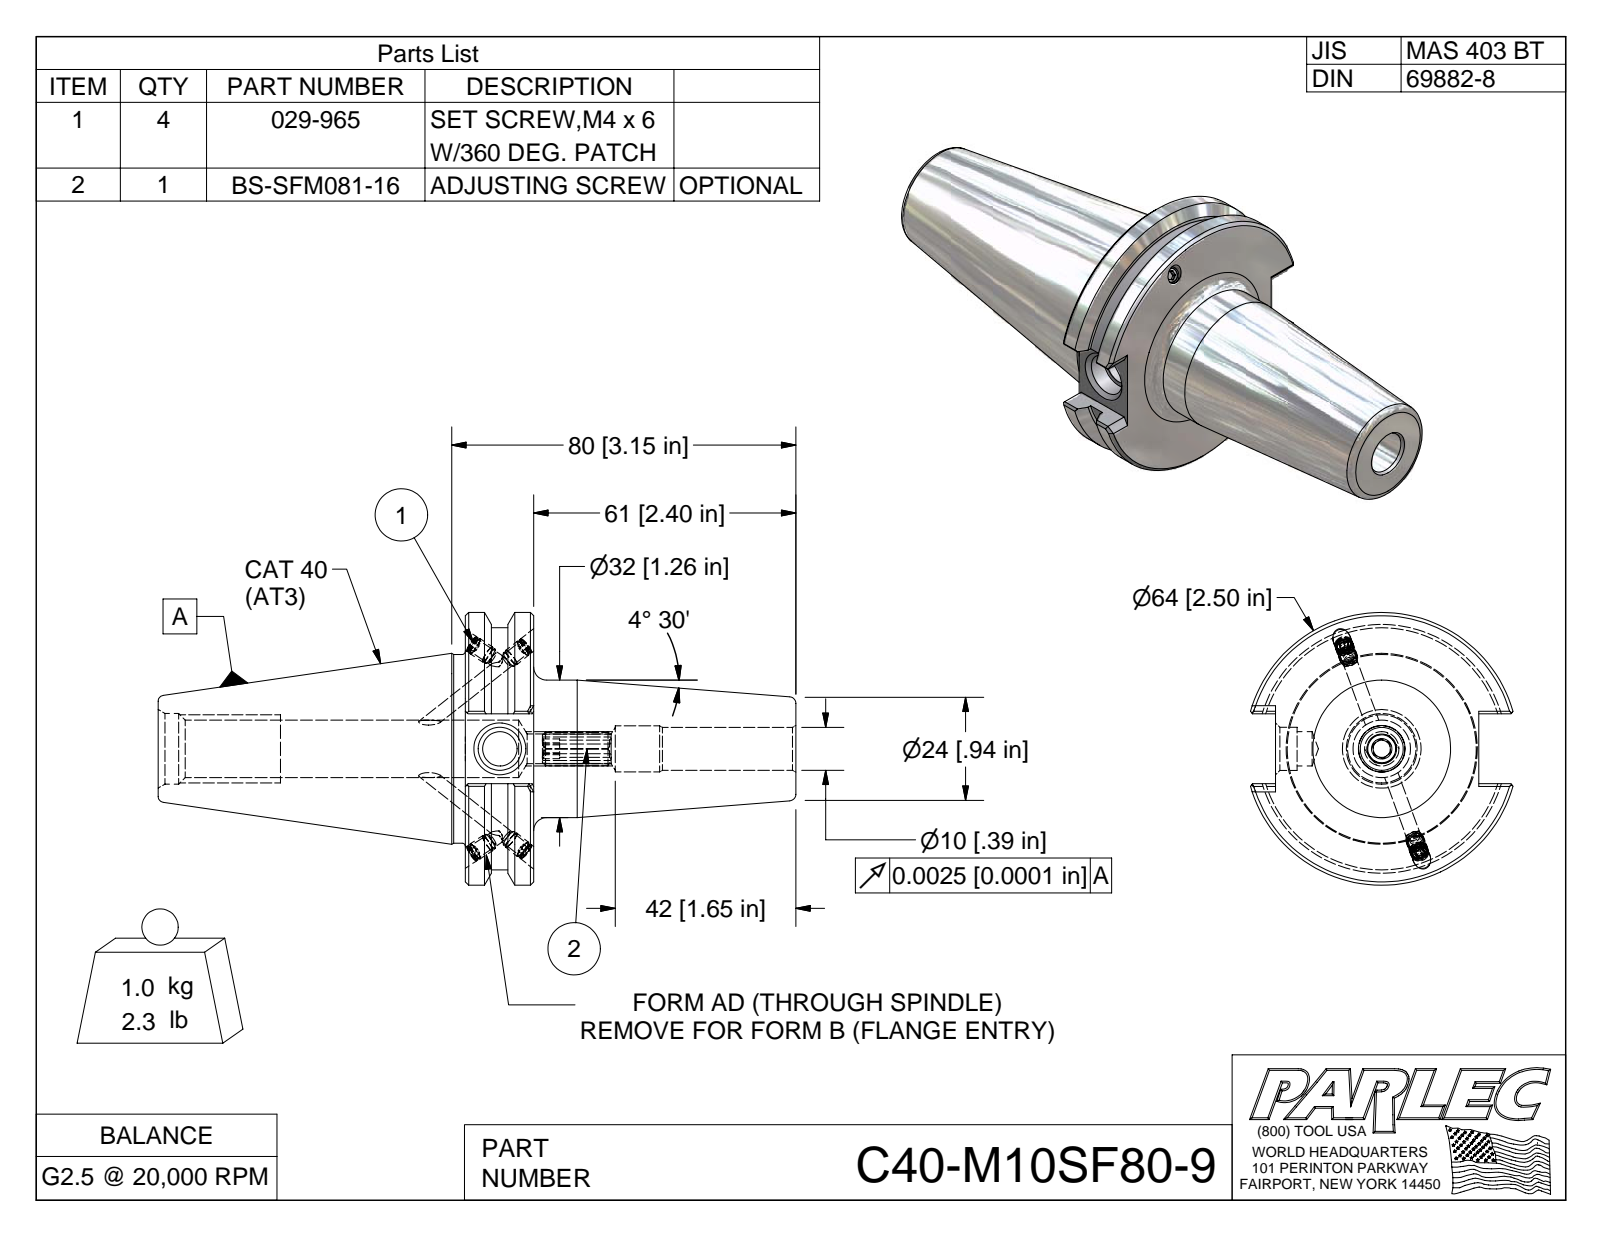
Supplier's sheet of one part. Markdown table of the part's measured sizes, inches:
| quantity | value |
| --- | --- |
| part name | C40-M10SF80-9; C40BC-M10SF80-9-1; 029-965; BS-SFM081-16 |
| STEP written by | Autodesk Inventor 2009 (AUTOMOTIVE_DESIGN) |
| units | inches |
| bodies | 6 solids, 172 faces (87 planar, 32 cylindrical, 53 other) |
| overall size | 5.837 × 2.5 × 2.403 |
| volume | 8.32 in³ |
| surface area | 44.78 in² |
| round holes (diameter × count) | 0.13 × 4, 0.161 × 4, 0.393 × 1, 0.423 × 1 |
| round bosses / shafts (diameter × count) | 0.165 × 4, 0.157 × 4, 2.5 × 1, 2.219 × 1, 1.73 × 1, 1.26 × 1 |
| partial cylindrical surfaces (radius × count) | 0.157 × 1 |
| main face-to-face distances | 0.625, 3.025, 2.4, 0.64, 1.86, 2.812, 3.437, 5.837, 3.201, 0.389 |
